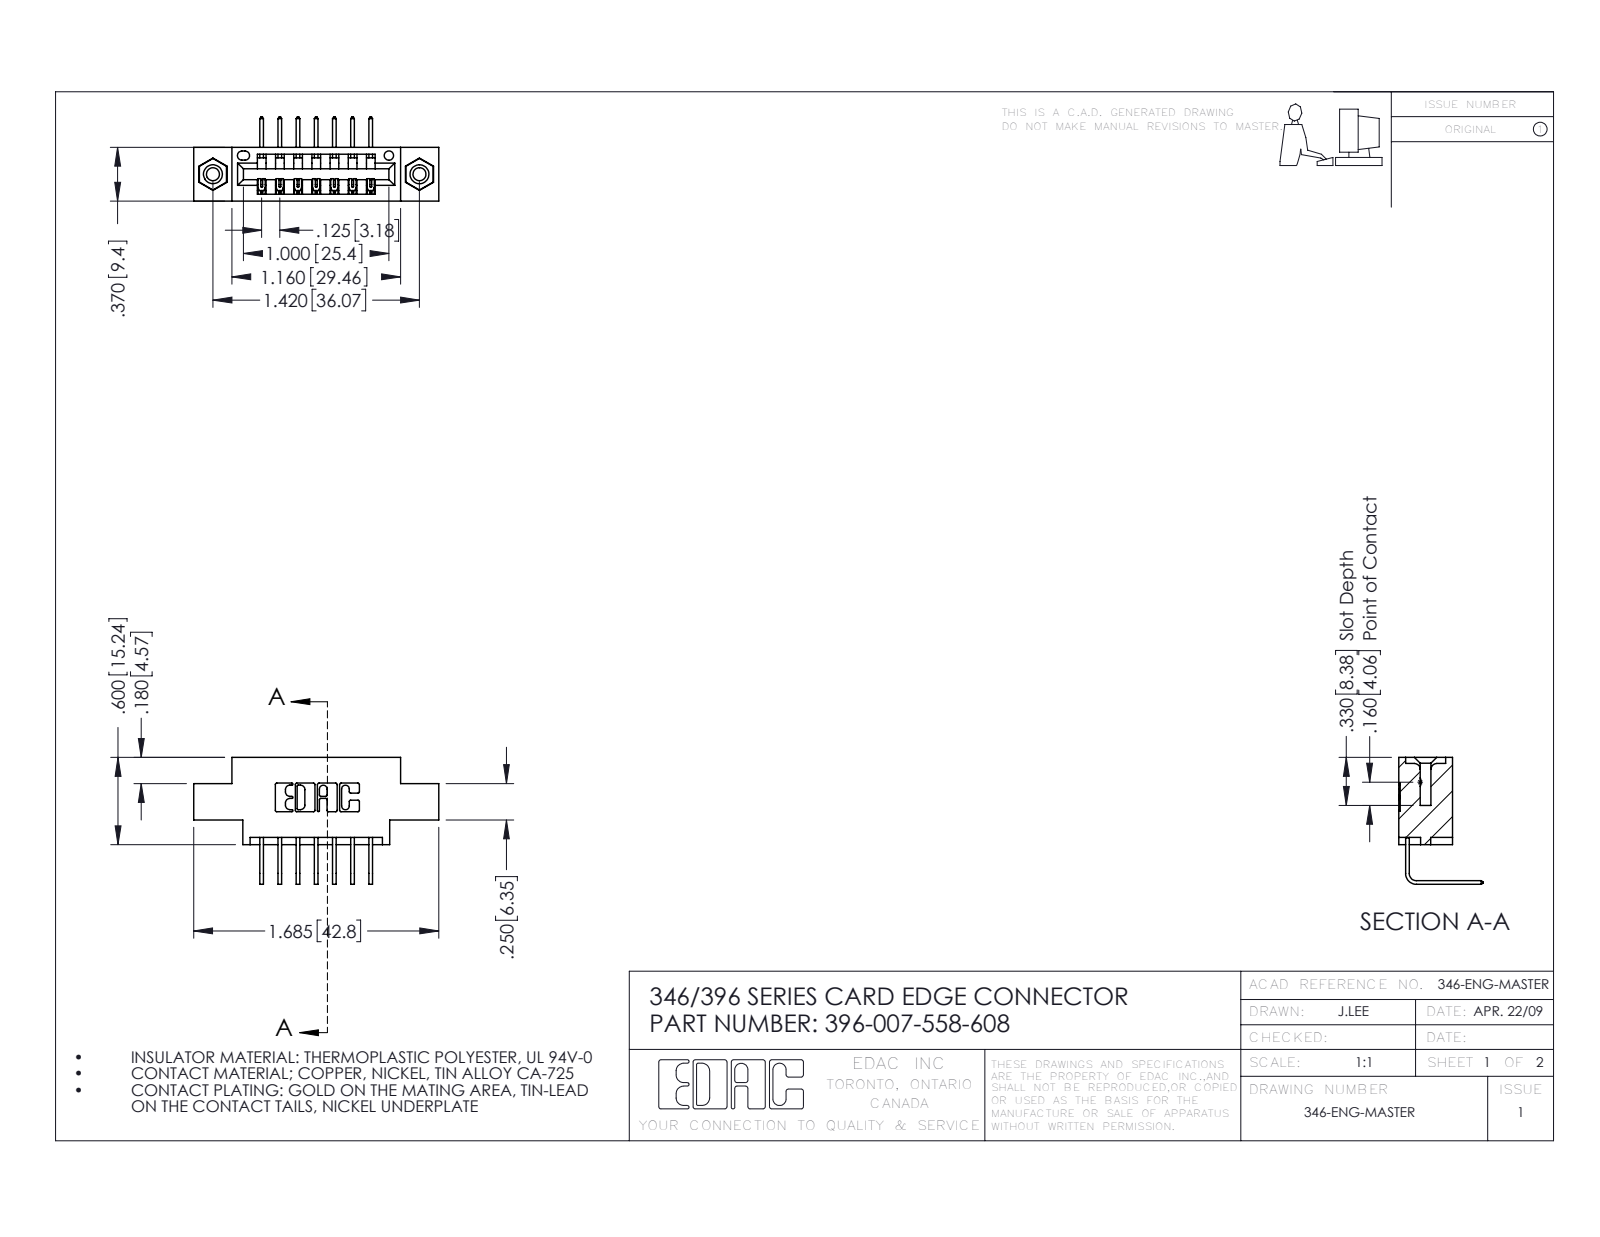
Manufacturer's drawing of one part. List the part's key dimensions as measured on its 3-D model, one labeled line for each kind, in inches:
Part name (STEP PRODUCT): 345-250-001_345-250-003-102; 345-292-001_558 Tail - 2; 396-007-558-608; 346 Part_0.170 Offset - 0.156 Dia-TI
STEP written by: SolidWorks 2016 (CONFIG_CONTROL_DESIGN)
Units: inches
Bodies: 10 solids, 606 faces (406 planar, 184 cylindrical, 16 other)
Overall size (bounding box): 1.685 × 0.873 × 0.58
Volume: 0.227 in³ · Surface area: 7.115 in²
Round holes (diameter × count): ⌀0.089 ×2, ⌀0.125 ×2, ⌀0.156 ×2, ⌀0.064 ×1
Round bosses / shafts (diameter × count): ⌀0.155 ×2
Partial cylindrical surfaces — rounded edges, fillets, slot ends (radius × count): R0.01 ×22, R0.006 ×14, R0.007 ×6, R0.031 ×6, R0.026 ×3, R0.031 ×2, R0.04 ×2, R0.014 ×1
Main face-to-face distances: 0.25, 0.37, 0.322, 0.048, 0.298, 0.025, 0.222, 0.148, 0.1, 0.174
Hole centre spacings: 0.246, 1.217, 1.42
